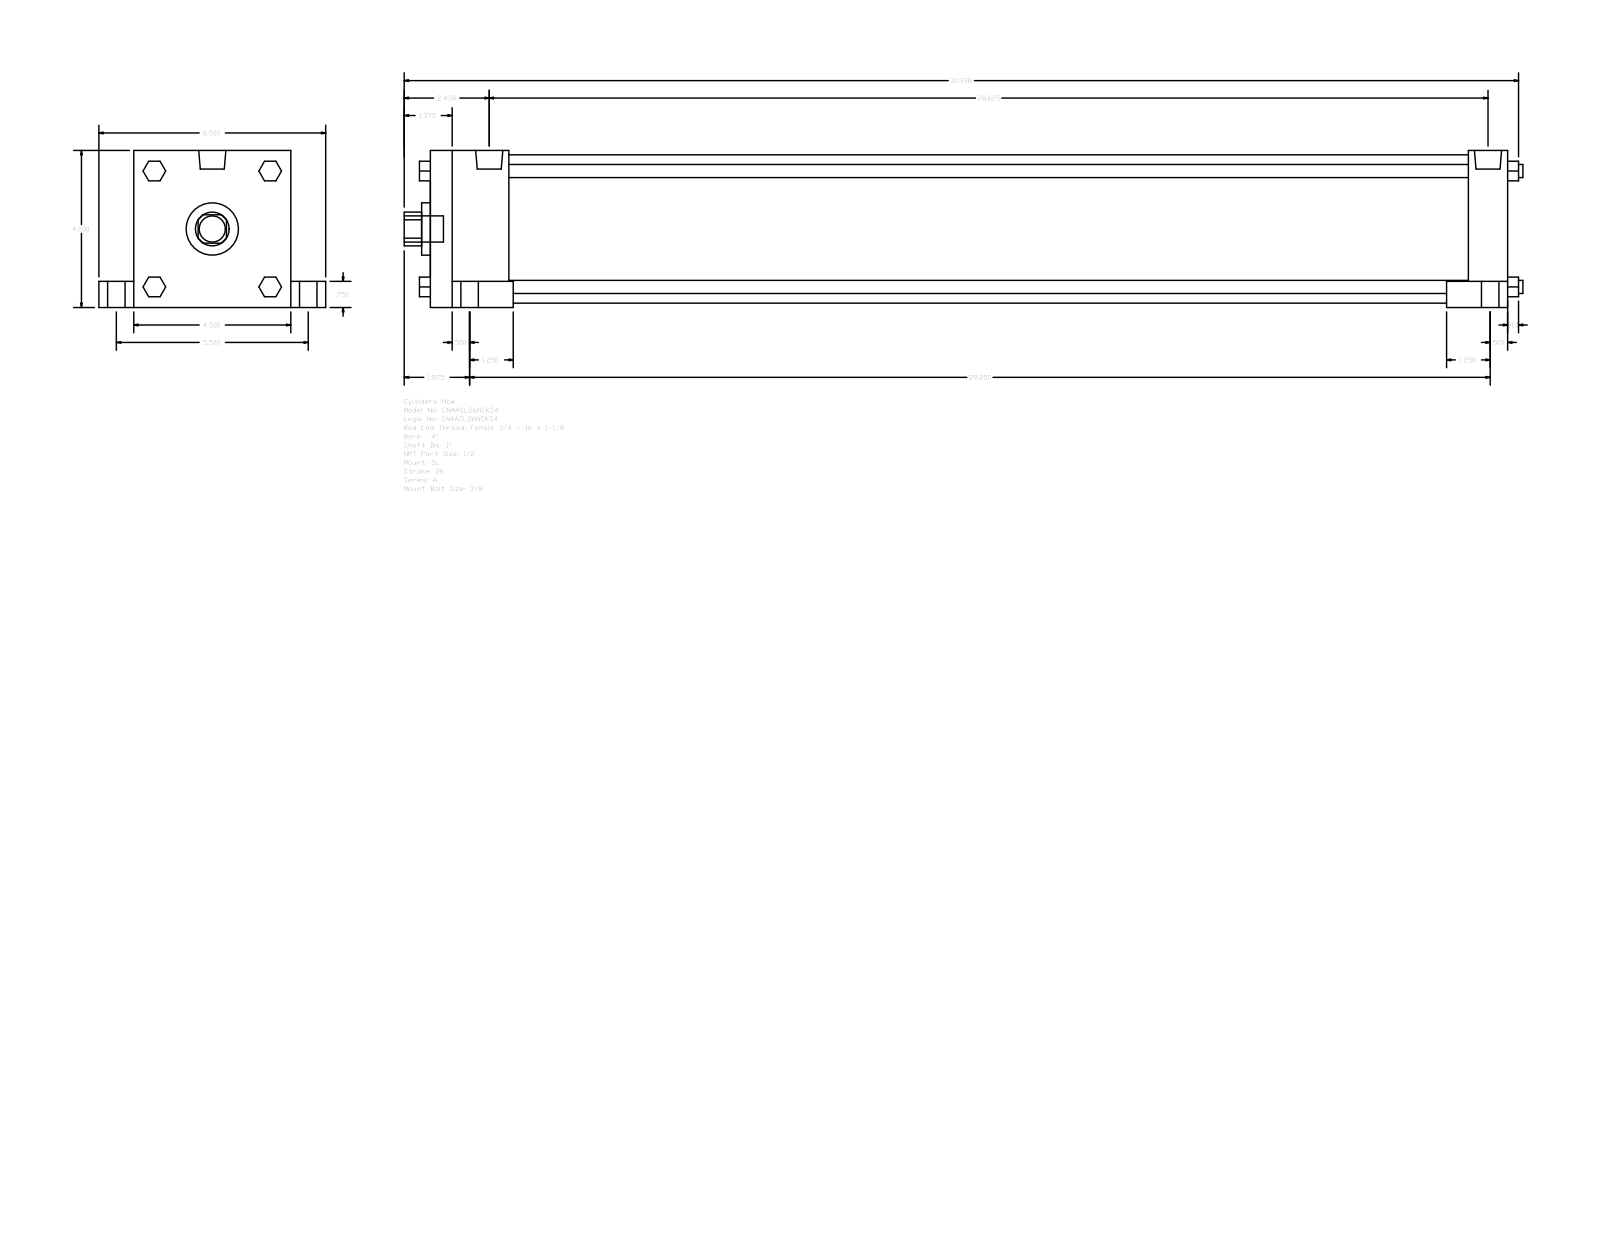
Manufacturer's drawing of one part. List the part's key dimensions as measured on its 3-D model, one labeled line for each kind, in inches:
Part name (STEP PRODUCT): A_SL__0400_1
STEP written by: GSSL Pune (CONFIG_CONTROL_DESIGN)
Units: inches
Bodies: 0 solids, 150 faces (114 planar, 36 cylindrical, 0 other)
Overall size (bounding box): 32.063 × 6.5 × 4.5
Round holes (diameter × count): ⌀1 ×1, ⌀1.5 ×1, ⌀4.25 ×1
Round bosses / shafts (diameter × count): ⌀0.75 ×5, ⌀0.5 ×4, ⌀0.375 ×4, ⌀0.344 ×4, ⌀0.778 ×2
Partial cylindrical surfaces — rounded edges, fillets, slot ends (radius × count): R0.484 ×1
Main face-to-face distances: 4.5, 30.875, 1.125, 2.25, 28.625, 29.75, 27.5, 0.75, 1, 5.5
